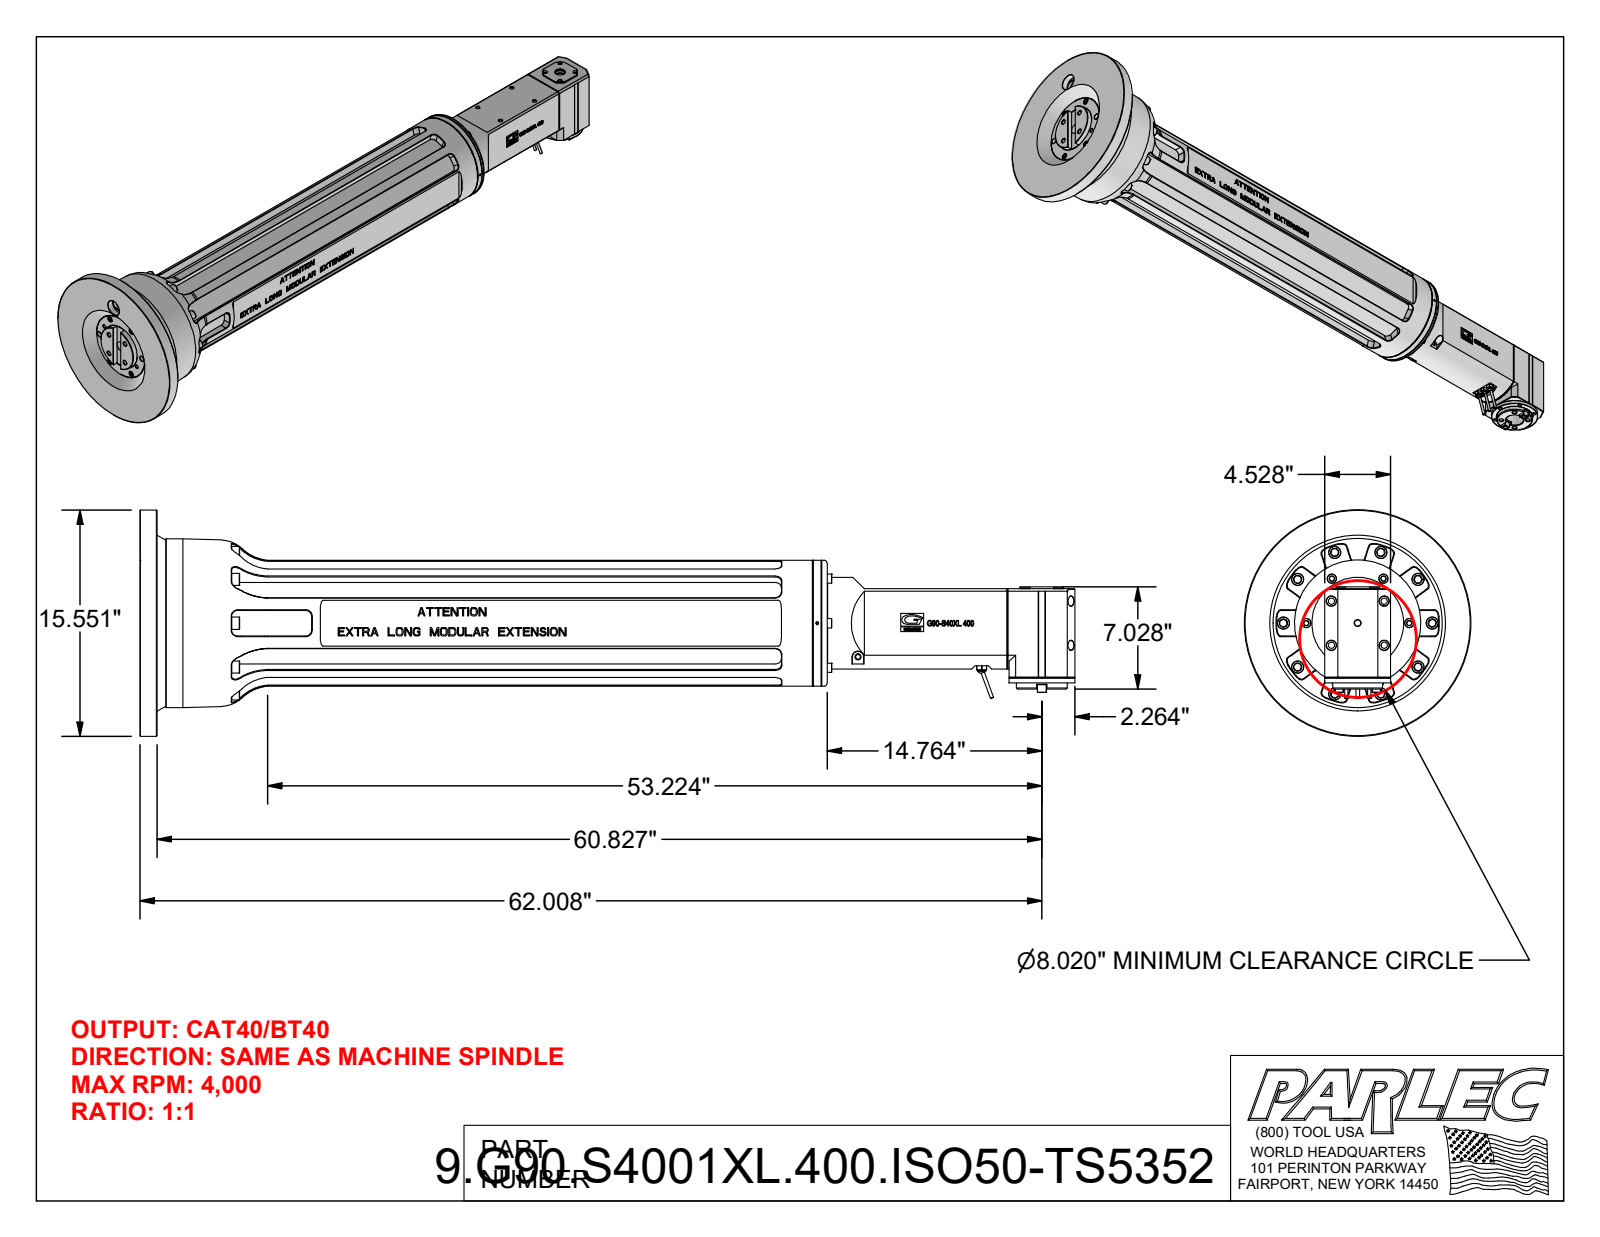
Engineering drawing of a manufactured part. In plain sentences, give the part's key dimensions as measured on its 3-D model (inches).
The part is named "9.G90.S4001XL.400.ISO50-TS5352; 9.UF.00006 (Classic, Universal Flange, Type 6)". Its 3-D file was written by "Autodesk Inventor 2022 (AUTOMOTIVE_DESIGN)". It is 15 solids with 4232 faces: 2456 planar, 631 cylindrical and 1145 other. Overall it measures 64.272 by 15.551 by 15.551 inches. Its volume is 2 564 cubic inches and its surface area 4 883 square inches. Round holes: 29 of diameter 0.551, 18 of diameter 0.268, 14 of diameter 0.197, 14 of diameter 0.335, 14 of diameter 0.354, 12 of diameter 0.472, 11 of diameter 0.591, 10 of diameter 0.165, 10 of diameter 0.217, 8 of diameter 0.346, 8 of diameter 0.413, 8 of diameter 0.748. Round bosses or shafts: 11 of diameter 0.551, 10 of diameter 0.827, 8 of diameter 0.709, 6 of diameter 0.63, 4 of diameter 0.512, 4 of diameter 0.315, 3 of diameter 0.236, 2 of diameter 2.165. Partial cylindrical surfaces (rounded edges, fillets, slot ends): 80 of radius 0.079, 36 of radius 0.433, 16 of radius 0.118, 10 of radius 0.728, 10 of radius 0.748, 7 of radius 0.394, 4 of radius 0.197, 3 of radius 0.386. The main face-to-face distances are 1.77, 1.772, 7.087, 7.086, 6.298, 1.771, 0.591, 8.069, 4.528, 1.181. The hole center spacings are 1.969, 2.953, 0.591, 2.362, 2.706, 3.937, 4.613, 1.394.
